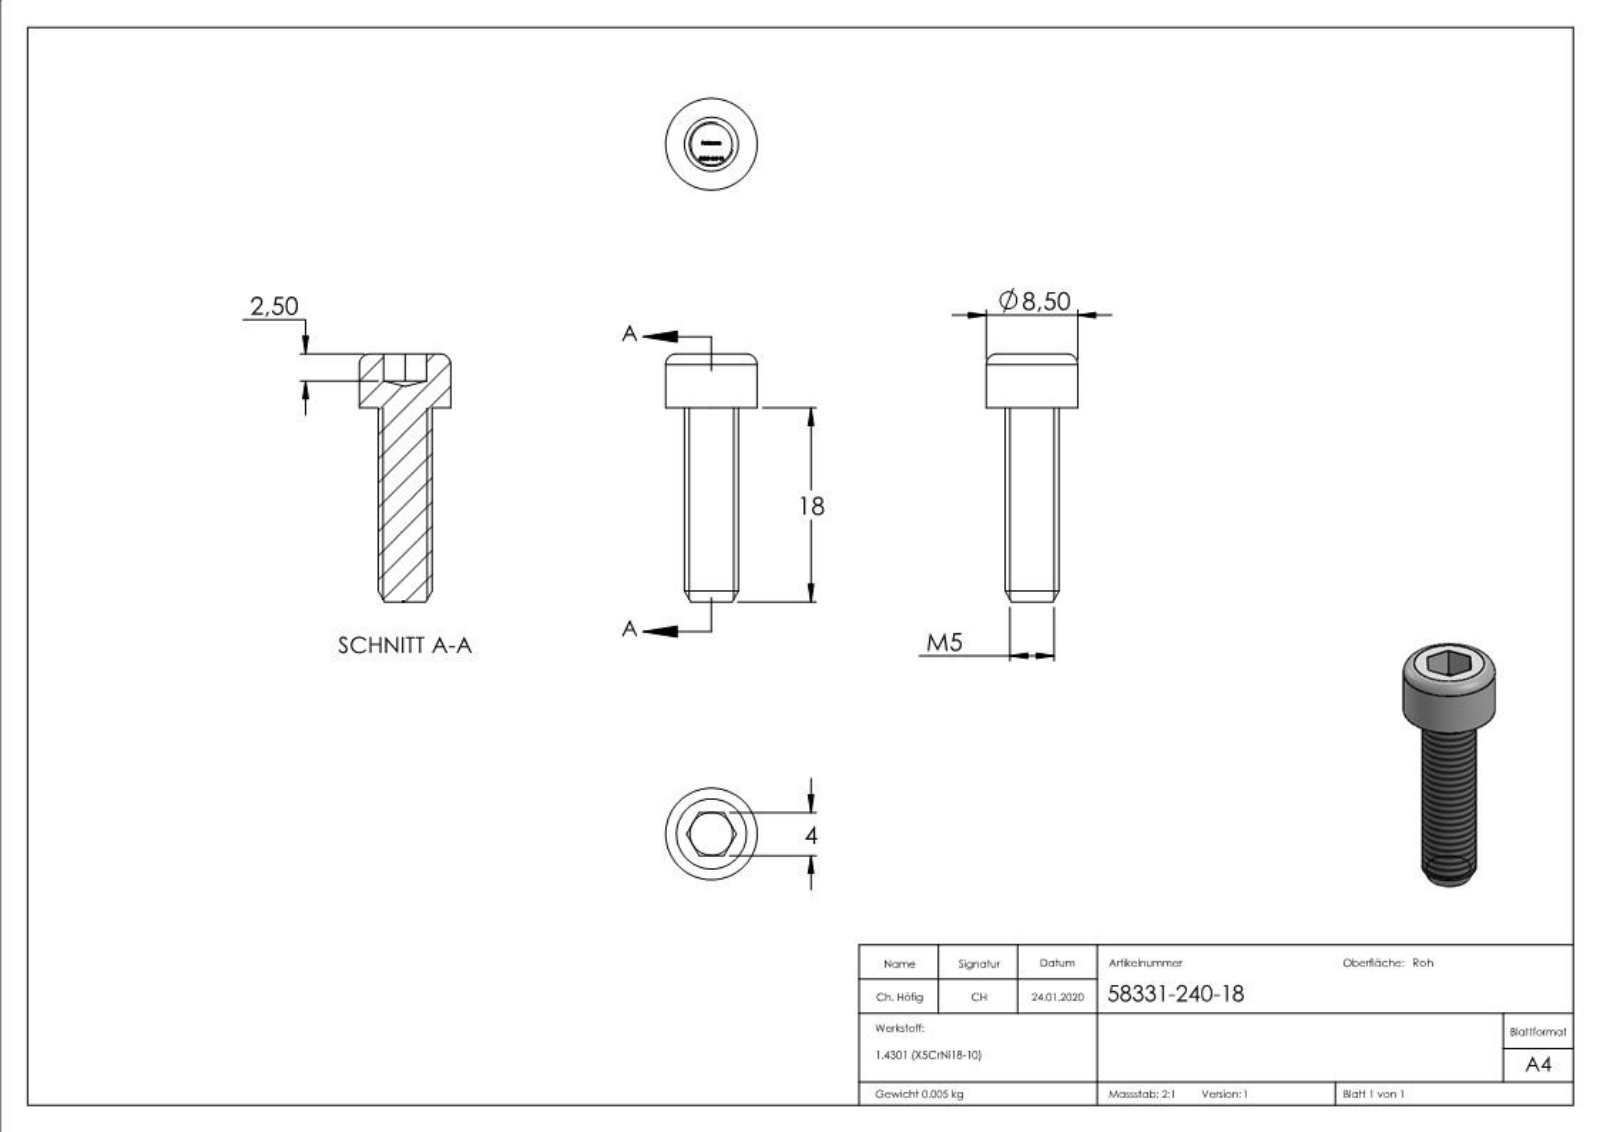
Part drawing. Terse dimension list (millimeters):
name: 58331-240-18
written by: SolidWorks 2015 (CONFIG_CONTROL_DESIGN)
unit: mm
bodies: 1 solid, 287 faces (149 planar, 2 cylindrical, 136 other)
size: 24 × 8.75 × 8.5
volume: 591 mm³; area: 547 mm²
bosses: 1× ⌀8.5, 1× ⌀5
face distances: 5, 4, 18, 23, 2.5, 20.5, 17.9, 20.4, 22.9, 0.65
